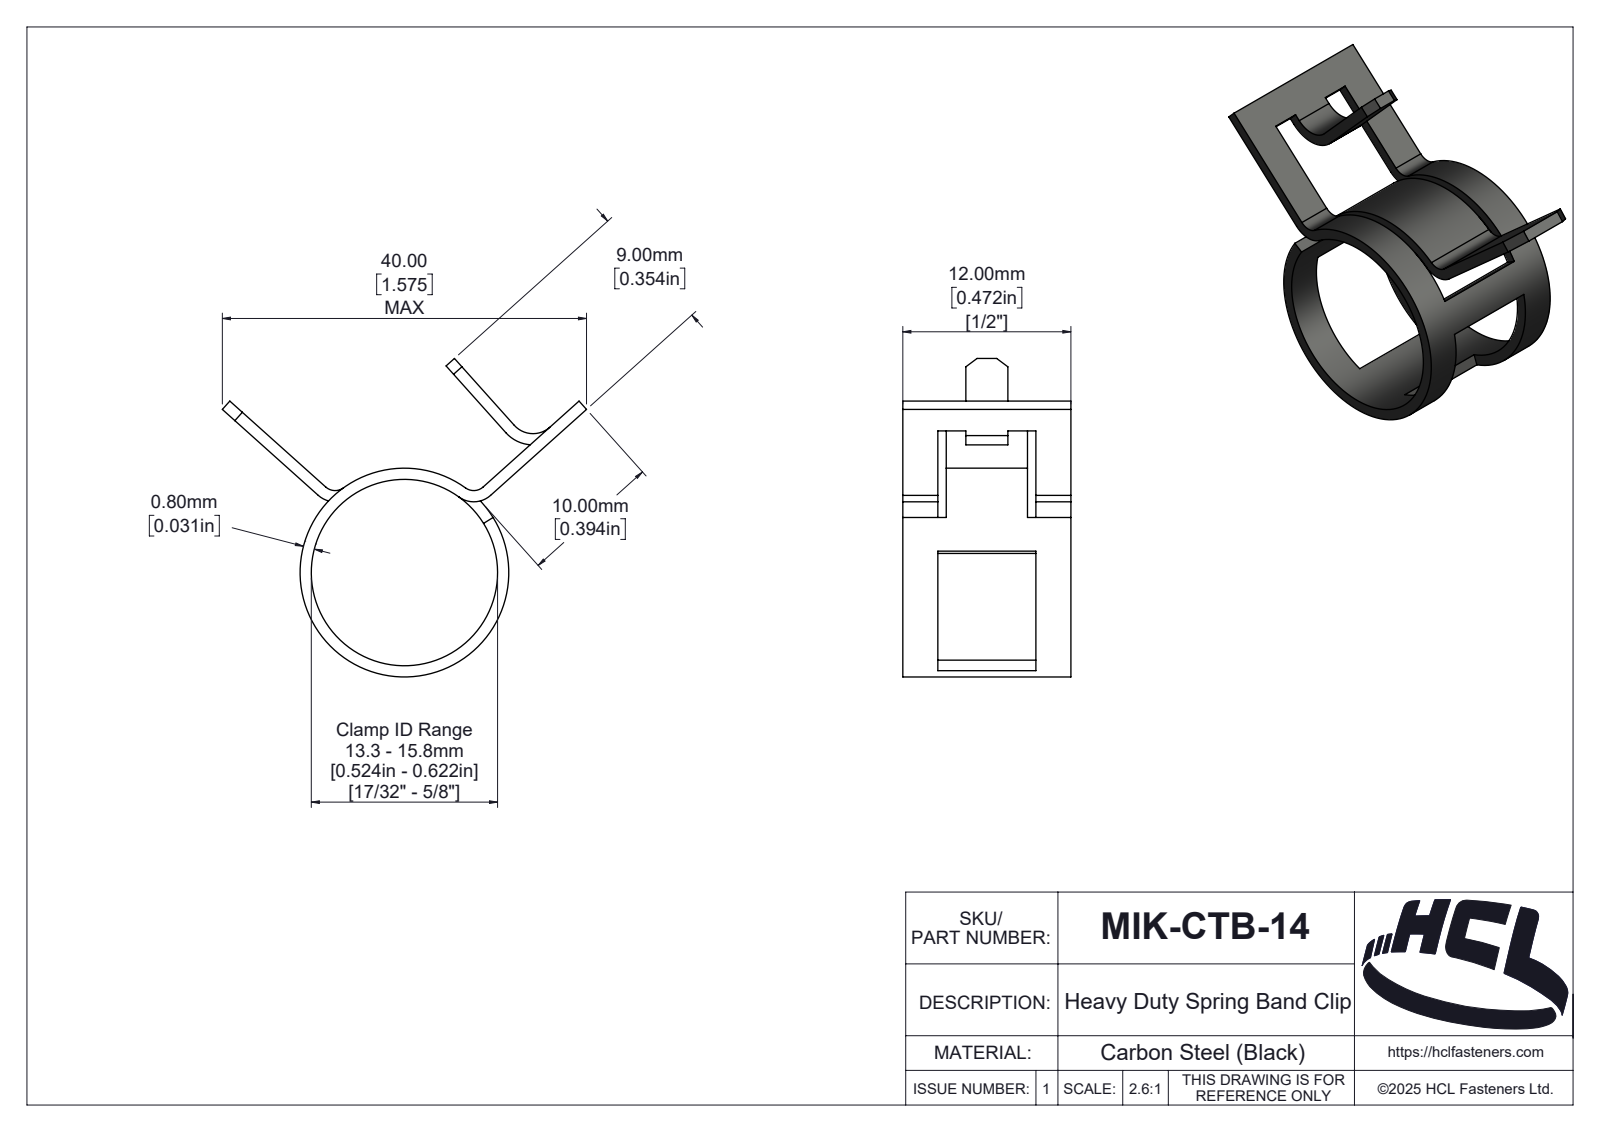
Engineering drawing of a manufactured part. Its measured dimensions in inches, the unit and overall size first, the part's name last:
Units: inches
Overall size (bounding box): 1.024 × 0.895 × 0.472
Round holes (diameter × count): ⌀0.524 ×1
Round bosses / shafts (diameter × count): ⌀0.587 ×1
Partial cylindrical surfaces — rounded edges, fillets, slot ends (radius × count): R0.071 ×3, R0.039 ×2, R0.013 ×1, R0.053 ×1, R0.066 ×1, R0.07 ×1, R0.084 ×1, R0.102 ×1
Main face-to-face distances: 0.031, 0.098, 0.374, 0.472, 0.122, 0.35, 0.024, 0.252, 0.276, 0.228
Volume: 0.025 in³ · Surface area: 1.978 in²
Bodies: 1 solid, 149 faces (36 planar, 64 cylindrical, 49 other)
Part name (STEP PRODUCT): MIK-CTB-14
STEP written by: SolidWorks 2025 (AUTOMOTIVE_DESIGN)
